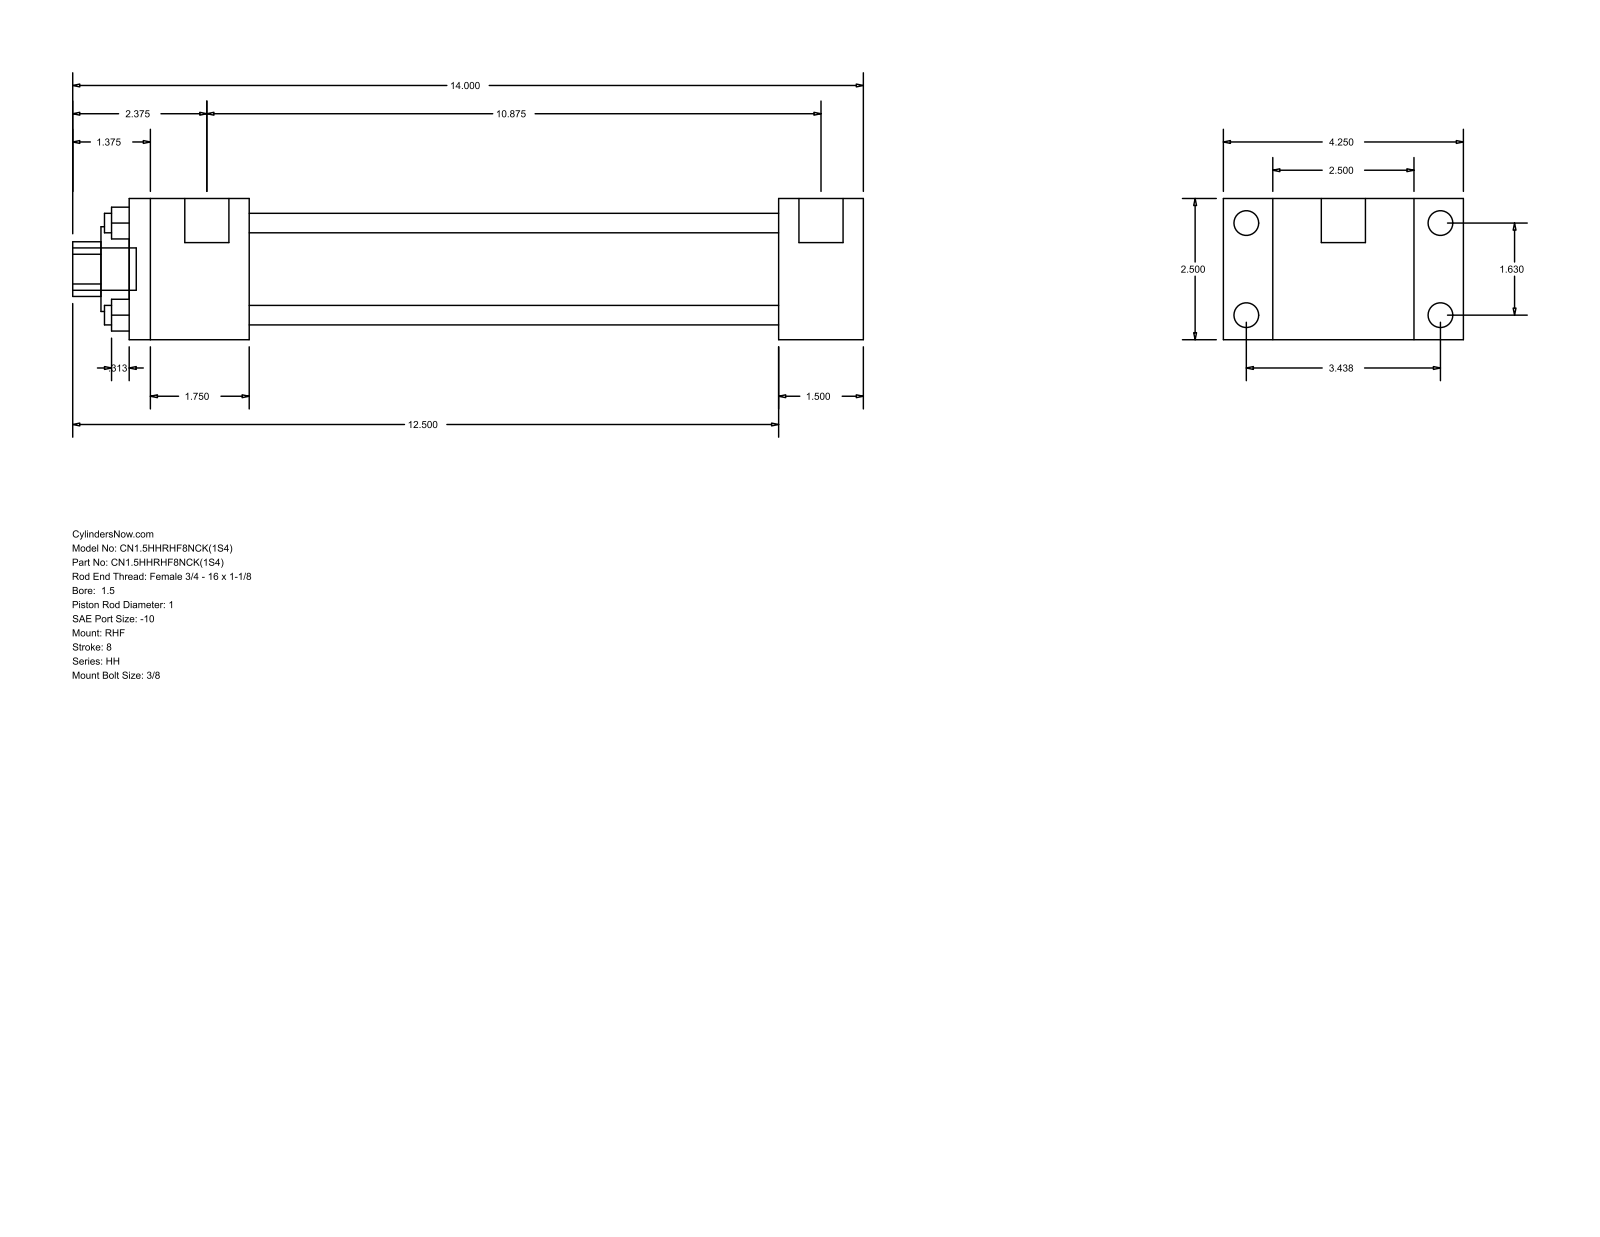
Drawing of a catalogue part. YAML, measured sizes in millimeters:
part_name: "HH_RHF__0150_1"
step_written_by: "GSSL Pune (CONFIG_CONTROL_DESIGN)"
units: millimeters
bodies: {solids: 0, faces: 88, planar: 60, cylindrical: 28, other: 0}
overall_size: [355.6, 107.95, 63.5]
round_holes:
  - {diameter: 8.76, count: 4}
  - {diameter: 25.4, count: 1}
  - {diameter: 38.1, count: 1}
  - {diameter: 44.45, count: 1}
round_bosses_or_shafts:
  - {diameter: 11.13, count: 4}
  - {diameter: 5.56, count: 4}
  - {diameter: 19.84, count: 2}
  - {diameter: 19.05, count: 1}
partial_cylinders:
  - {radius: 12.29, count: 1}
face_to_face_distances: [63.5, 22.23, 85.73, 38.1, 107.96, 238.12, 276.22, 53.98, 292.1, 330.2]
hole_center_spacings: [29.27, 41.4, 58.55]
